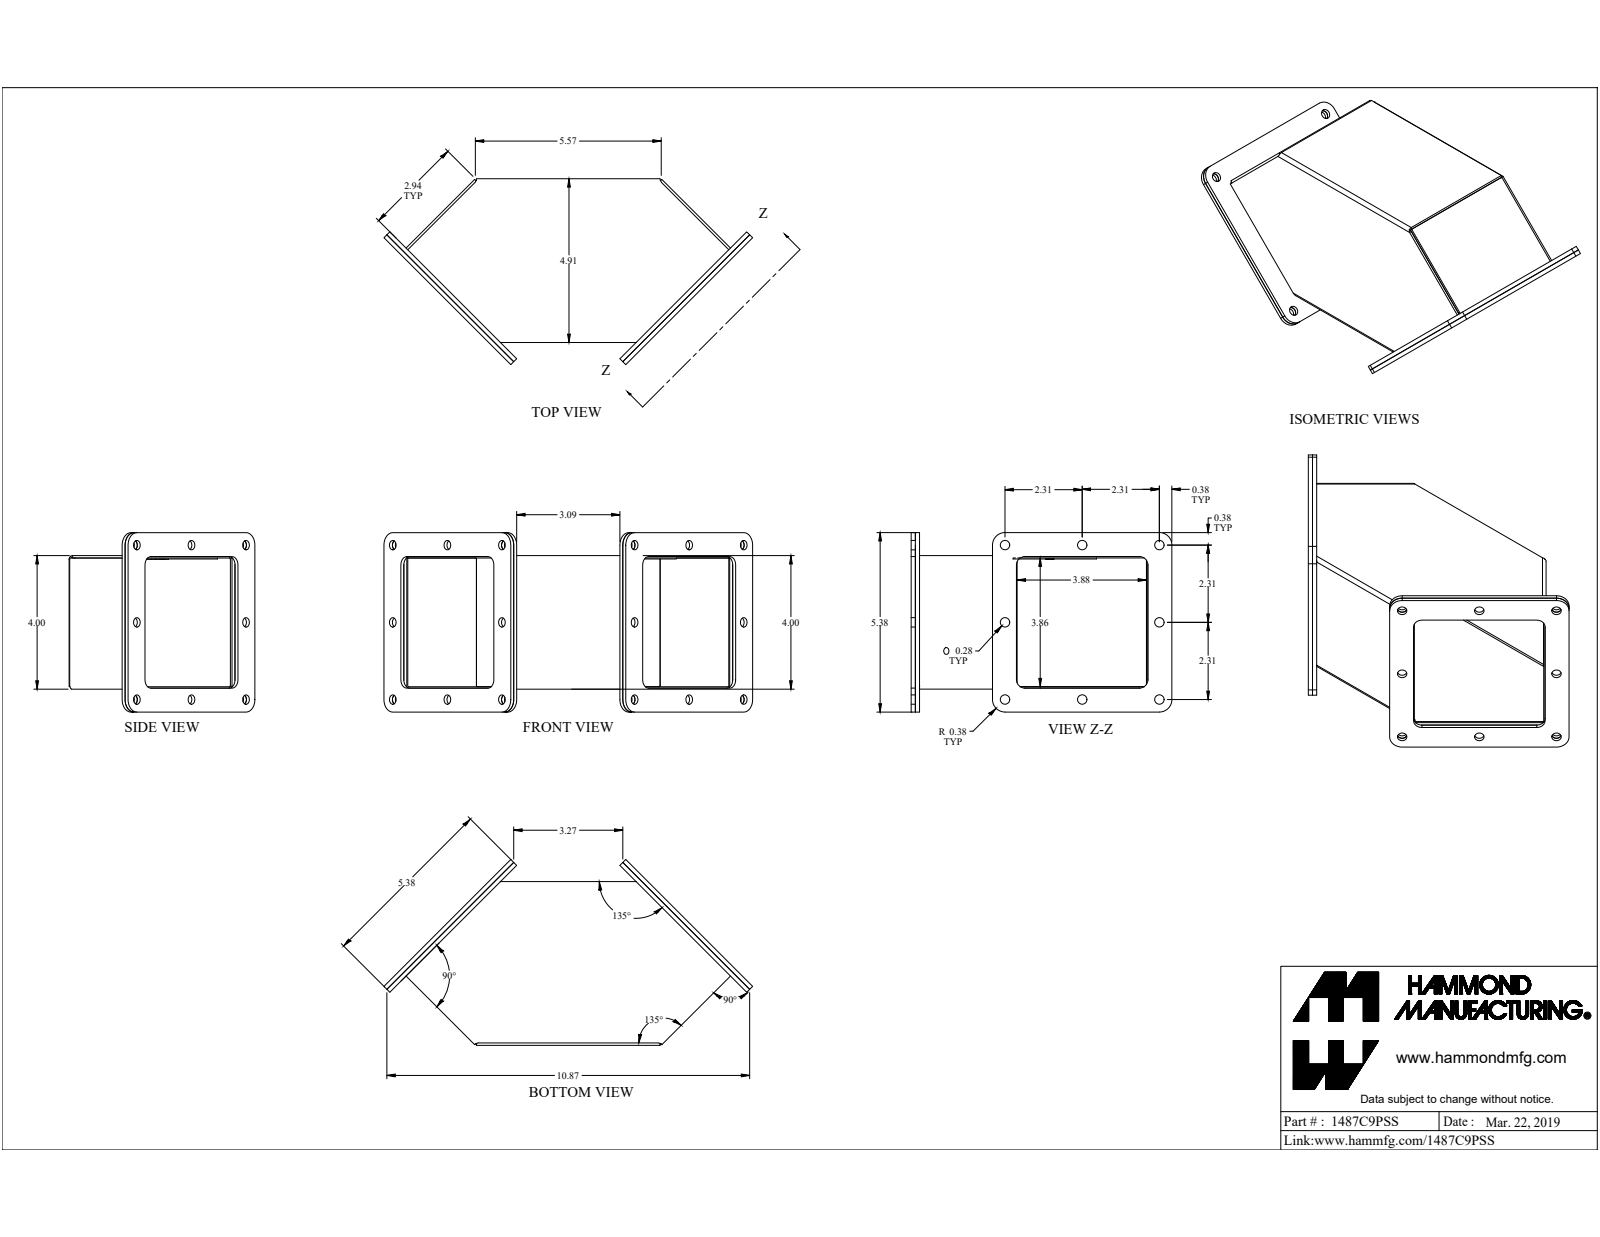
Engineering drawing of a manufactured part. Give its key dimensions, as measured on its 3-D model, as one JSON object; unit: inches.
{"part_name": "1487C9PSS", "step_written_by": "SolidWorks 2019 (CONFIG_CONTROL_DESIGN)", "units": "inches", "bodies": {"solids": 12, "faces": 395, "planar": 238, "cylindrical": 114, "other": 43}, "overall_size": [11.073, 5.59, 5.375], "volume_in3": 16.2, "surface_area_in2": 410.8, "round_holes": [[0.281, 18], [0.196, 2], [0.258, 2], [0.35, 2]], "round_bosses_or_shafts": [[0.5, 2], [0.25, 2]], "partial_cylinders_radius": [[0.375, 14], [0.02, 12], [0.25, 8], [0.036, 5], [0.108, 5], [0.062, 4], [0.063, 4]], "face_to_face_distances": [0.072, 3.928, 3.856, 4, 4.833, 0.125, 0.25, 0.125, 7.052, 6.926], "hole_center_spacings": [2.313, 4.625, 5.171, 3.27, 5.171, 6.541, 2.312, 4.625]}
